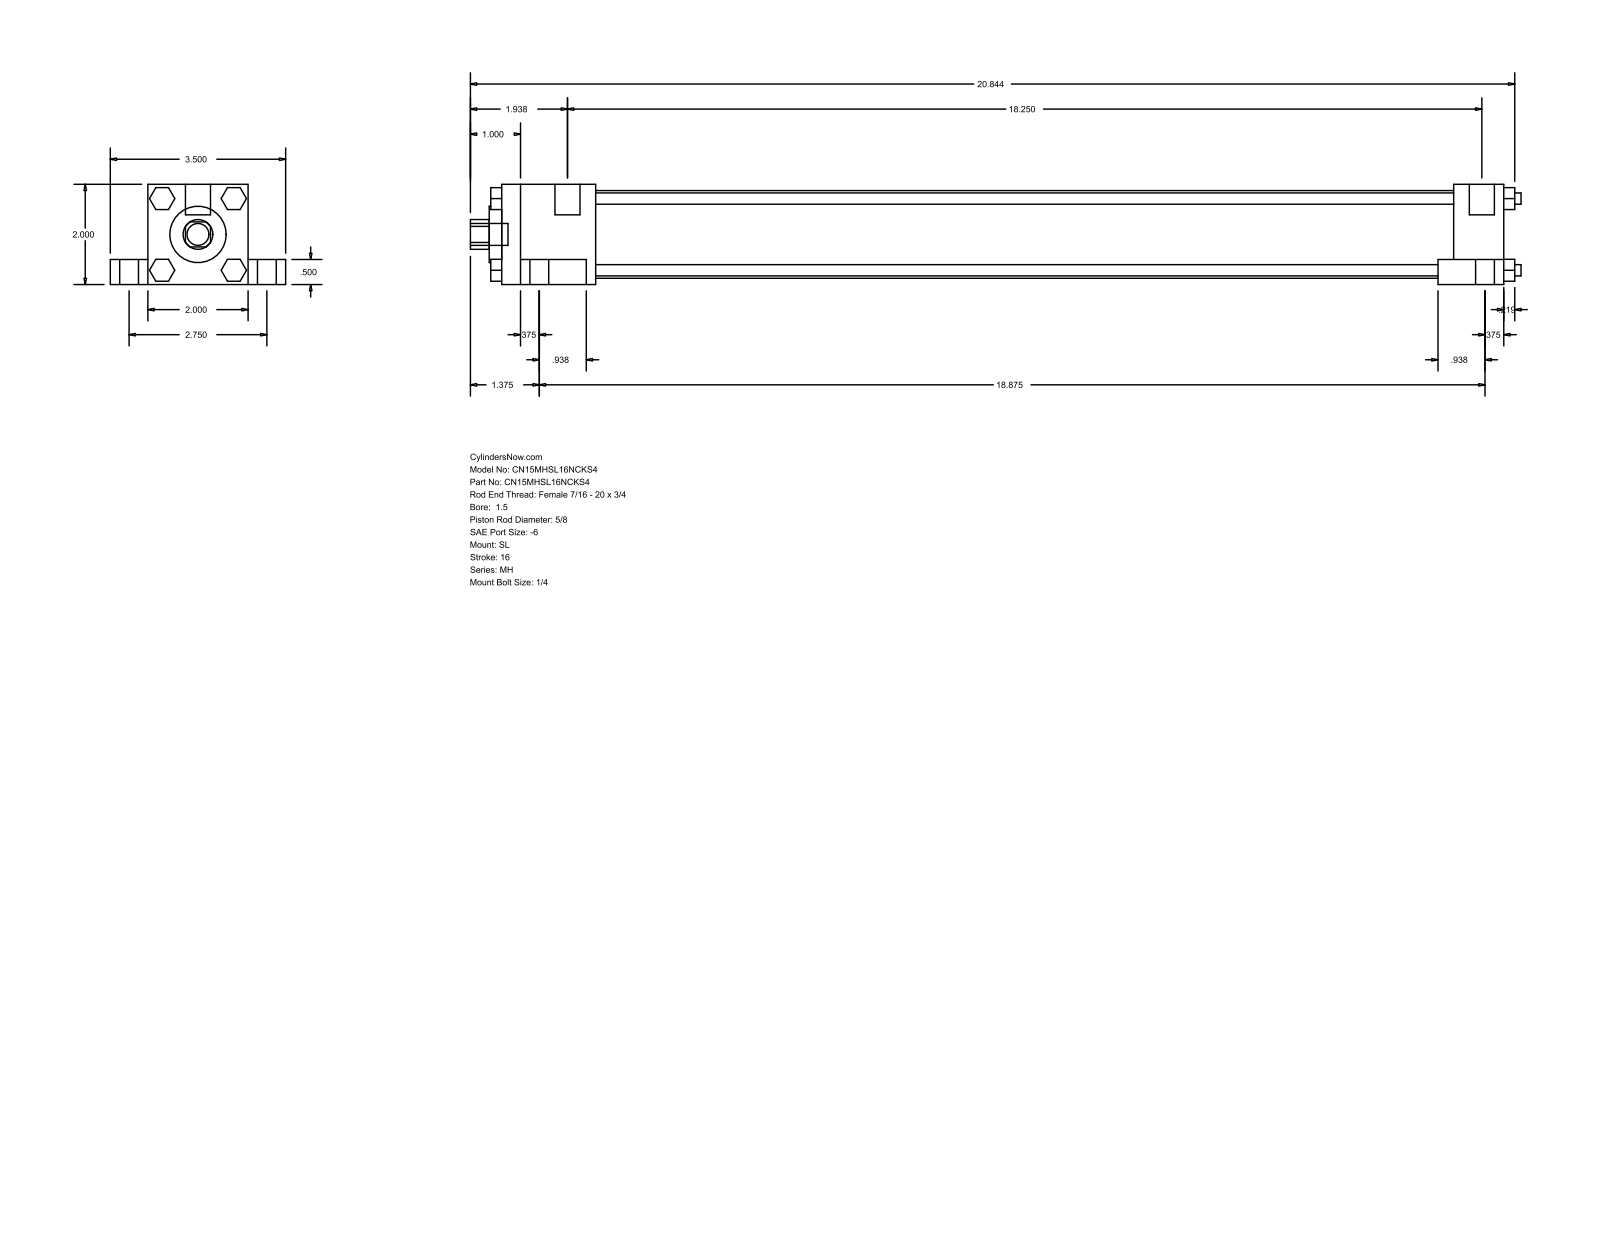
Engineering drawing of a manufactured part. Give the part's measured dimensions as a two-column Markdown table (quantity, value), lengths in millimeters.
| quantity | value |
| --- | --- |
| part name | MH_SL__0150_0.625 |
| STEP written by | GSSL Pune (CONFIG_CONTROL_DESIGN) |
| units | millimeters |
| bodies | 0 solids, 148 faces (112 planar, 36 cylindrical, 0 other) |
| overall size | 532.61 × 88.9 × 50.8 |
| round holes (diameter × count) | 15.88 × 1, 28.57 × 1, 44.45 × 1 |
| round bosses / shafts (diameter × count) | 15.88 × 4, 9.53 × 4, 5.71 × 4, 5.56 × 4, 12.7 × 2, 11.11 × 1 |
| partial cylindrical surfaces (radius × count) | 7.54 × 1 |
| main face-to-face distances | 50.8, 38.1, 19.05, 12.7, 69.85, 508, 9.52, 25.4, 33.34, 465.14 |
